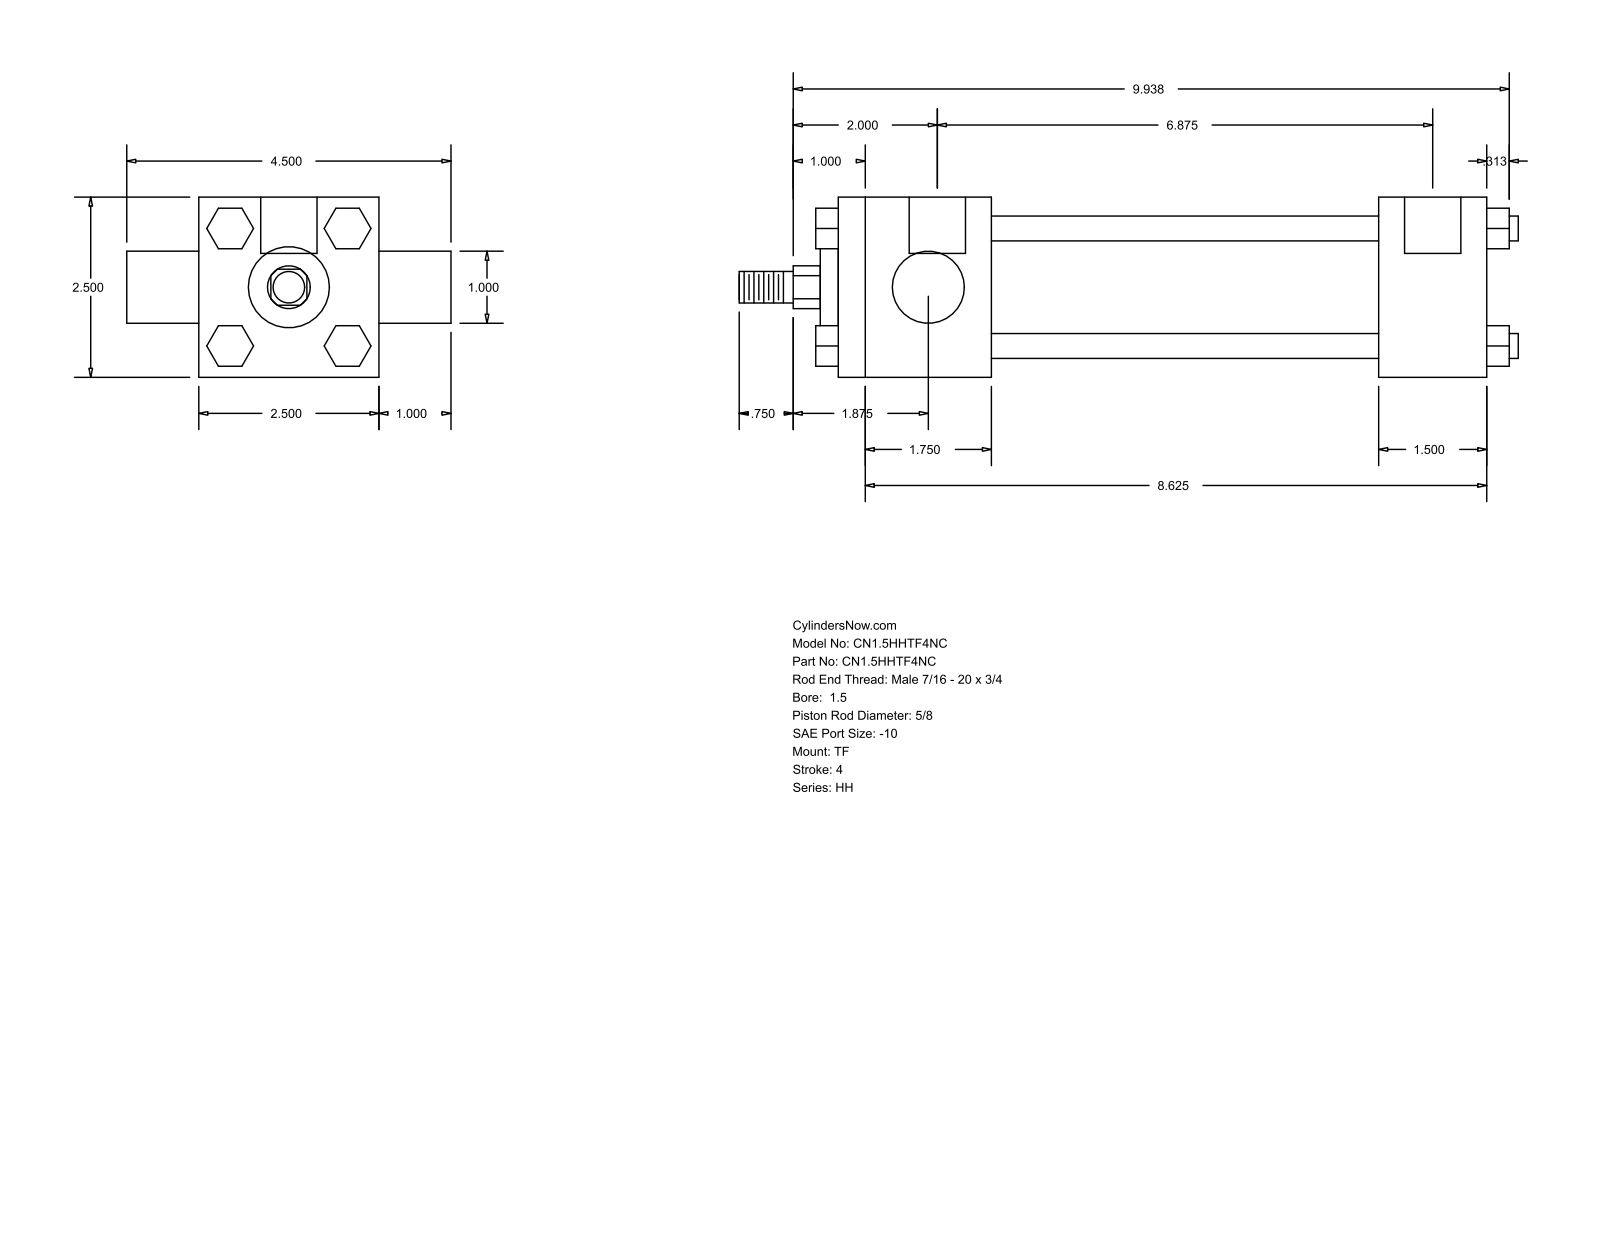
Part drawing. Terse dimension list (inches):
name: HH_TF__0150_0.625
written by: GSSL Pune (CONFIG_CONTROL_DESIGN)
unit: in
bodies: 0 solids, 120 faces (92 planar, 28 cylindrical, 0 other)
size: 10.813 × 4.5 × 2.5
holes: 3× ⌀0.219, 2× ⌀0.781
bosses: 4× ⌀0.345, 1× ⌀1.75, 1× ⌀1.125, 1× ⌀1, 1× ⌀0.625, 1× ⌀0.437
rounds: 1× R0.297
face distances: 2.5, 9, 2.125, 6.875, 7.5, 5.375, 1.5, 1, 3.5, 0.815
hole spacings: 0.062, 0.063, 6.875, 6.937, 6.938, 7
